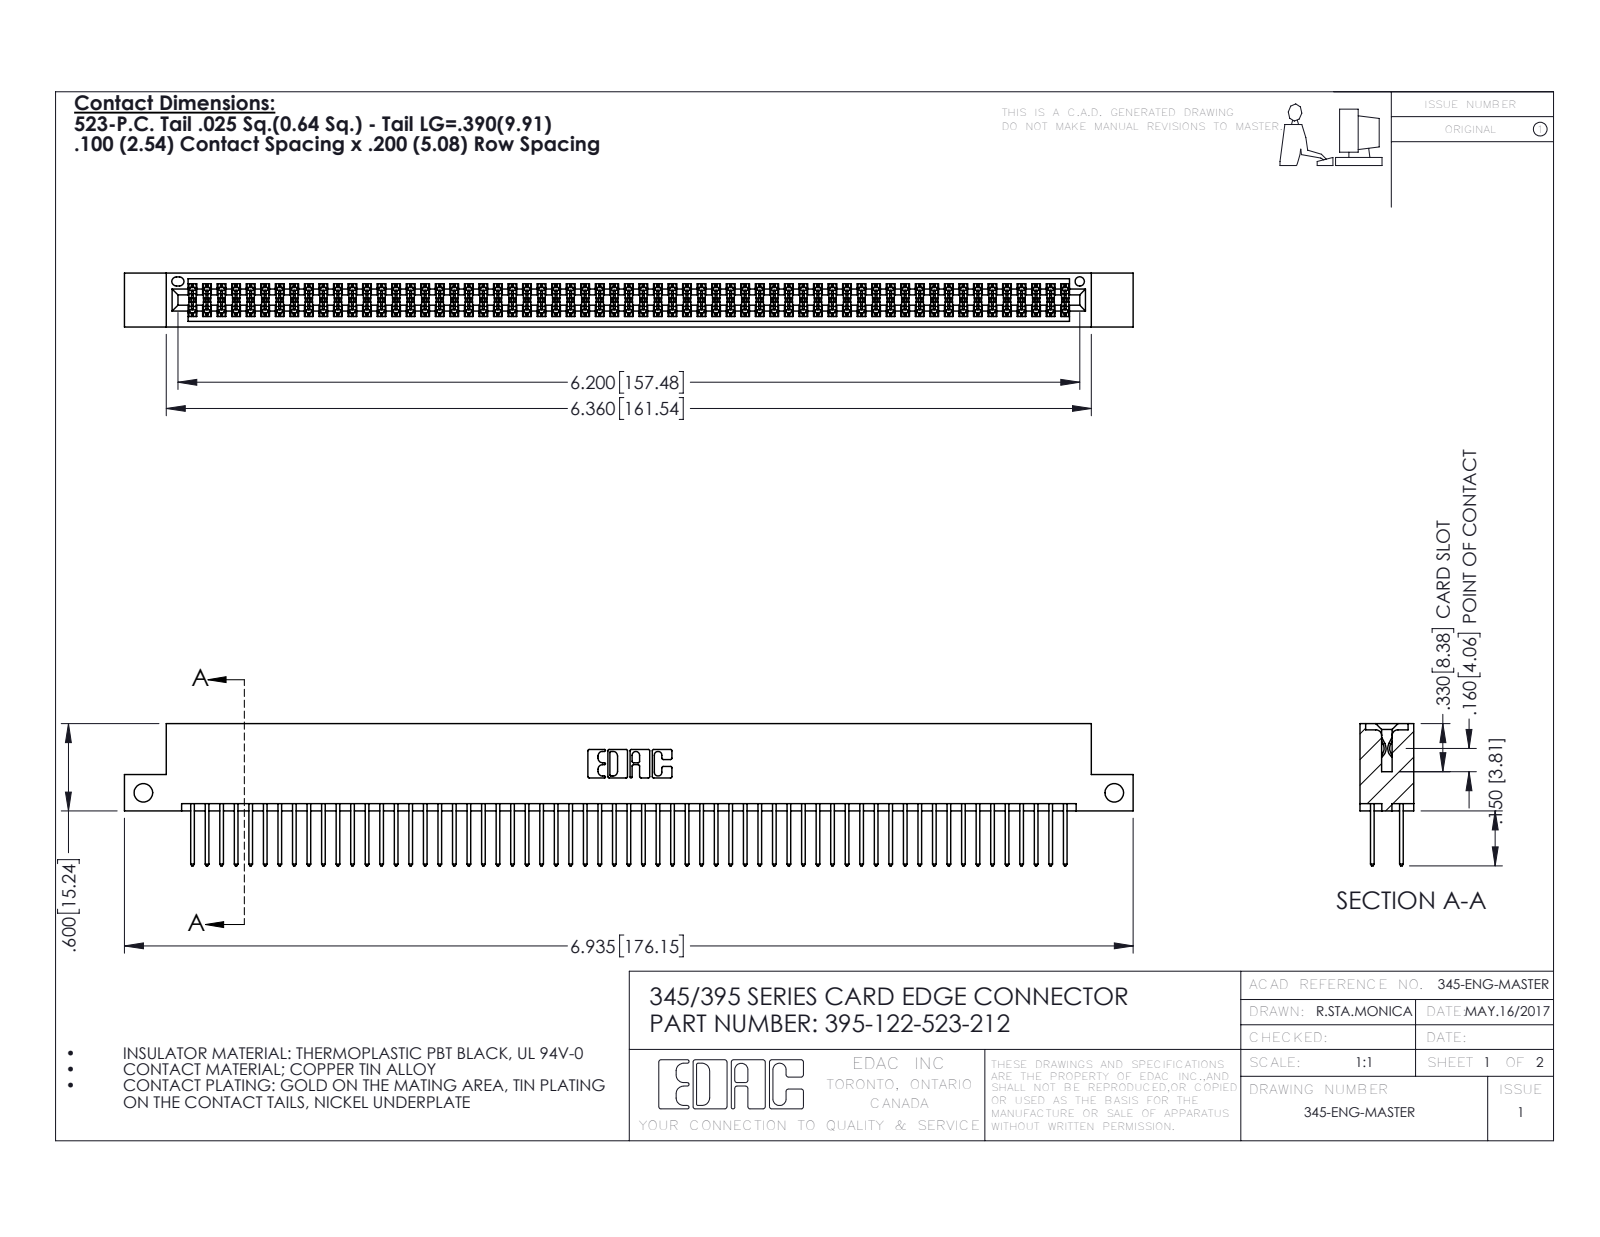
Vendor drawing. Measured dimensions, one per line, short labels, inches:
name: 345 Part_Flush Mounting Lugs - Side Mount; 345-292-001_345-293-123; 395-122-523-212
written by: SolidWorks 2016 (CONFIG_CONTROL_DESIGN)
unit: in
bodies: 123 solids, 6226 faces (4106 planar, 2120 cylindrical, 0 other)
size: 6.935 × 0.977 × 0.37
volume: 1.065 in³; area: 42.08 in²
holes: 2× ⌀0.128, 1× ⌀0.064
rounds: 183× R0.006, 122× R0.01, 22× R0.01, 6× R0.007, 6× R0.031, 3× R0.026, 2× R0.014, 2× R0.019
face distances: 0.298, 0.072, 0.2, 0.098, 0.272, 0.025, 0.37, 0.225, 0.175, 0.149
hole spacings: 6.675
